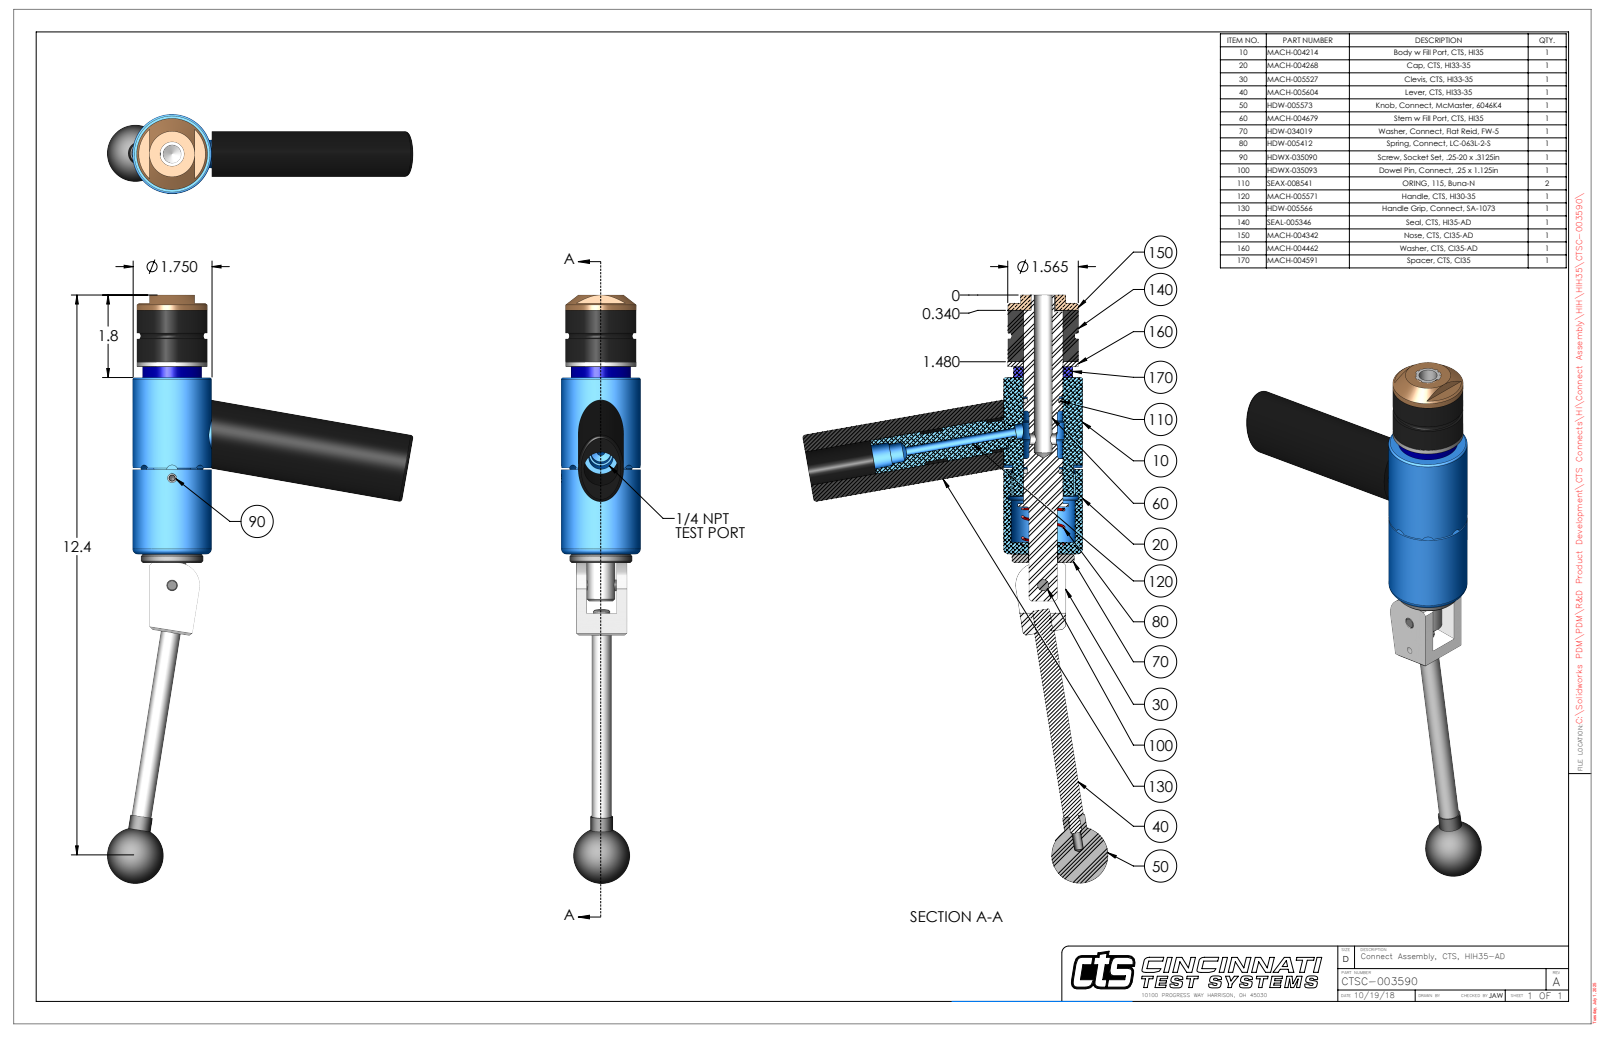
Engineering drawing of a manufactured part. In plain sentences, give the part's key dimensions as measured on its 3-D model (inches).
The part is named "CTSC-003590". Its 3-D file was written by "SolidWorks 2023 (AUTOMOTIVE_DESIGN)". It is 12 solids with 309 faces: 110 planar, 128 cylindrical and 71 other. Overall it measures 13.042 by 6.763 by 1.75 inches. Its volume is 19.63 cubic inches and its surface area 129.7 square inches. Round holes: 2 of diameter 0.201, 1 of diameter 0.15, 1 of diameter 0.187, 1 of diameter 0.249, 1 of diameter 0.25, 1 of diameter 0.251, 1 of diameter 0.313, 1 of diameter 0.406, 1 of diameter 0.438, 1 of diameter 0.531, 1 of diameter 0.635, 1 of diameter 0.656. Round bosses or shafts: 2 of diameter 0.25, 1 of diameter 1.75, 1 of diameter 1.565, 1 of diameter 1.565, 1 of diameter 1.38, 1 of diameter 1.312, 1 of diameter 0.869, 1 of diameter 0.75. Partial cylindrical surfaces (rounded edges, fillets, slot ends): 4 of radius 0.125, 2 of radius 0.029, 1 of radius 0.166, 1 of radius 0.166, 1 of radius 0.242, 1 of radius 0.33, 1 of radius 0.5, 1 of radius 0.695. The main face-to-face distances are 1.14, 5.405, 4.265, 1.49, 0.35, 3.915, 1.25, 0.11, 0.24, 4.155. The hole center spacings are 0.74, 2.376, 3.116.
